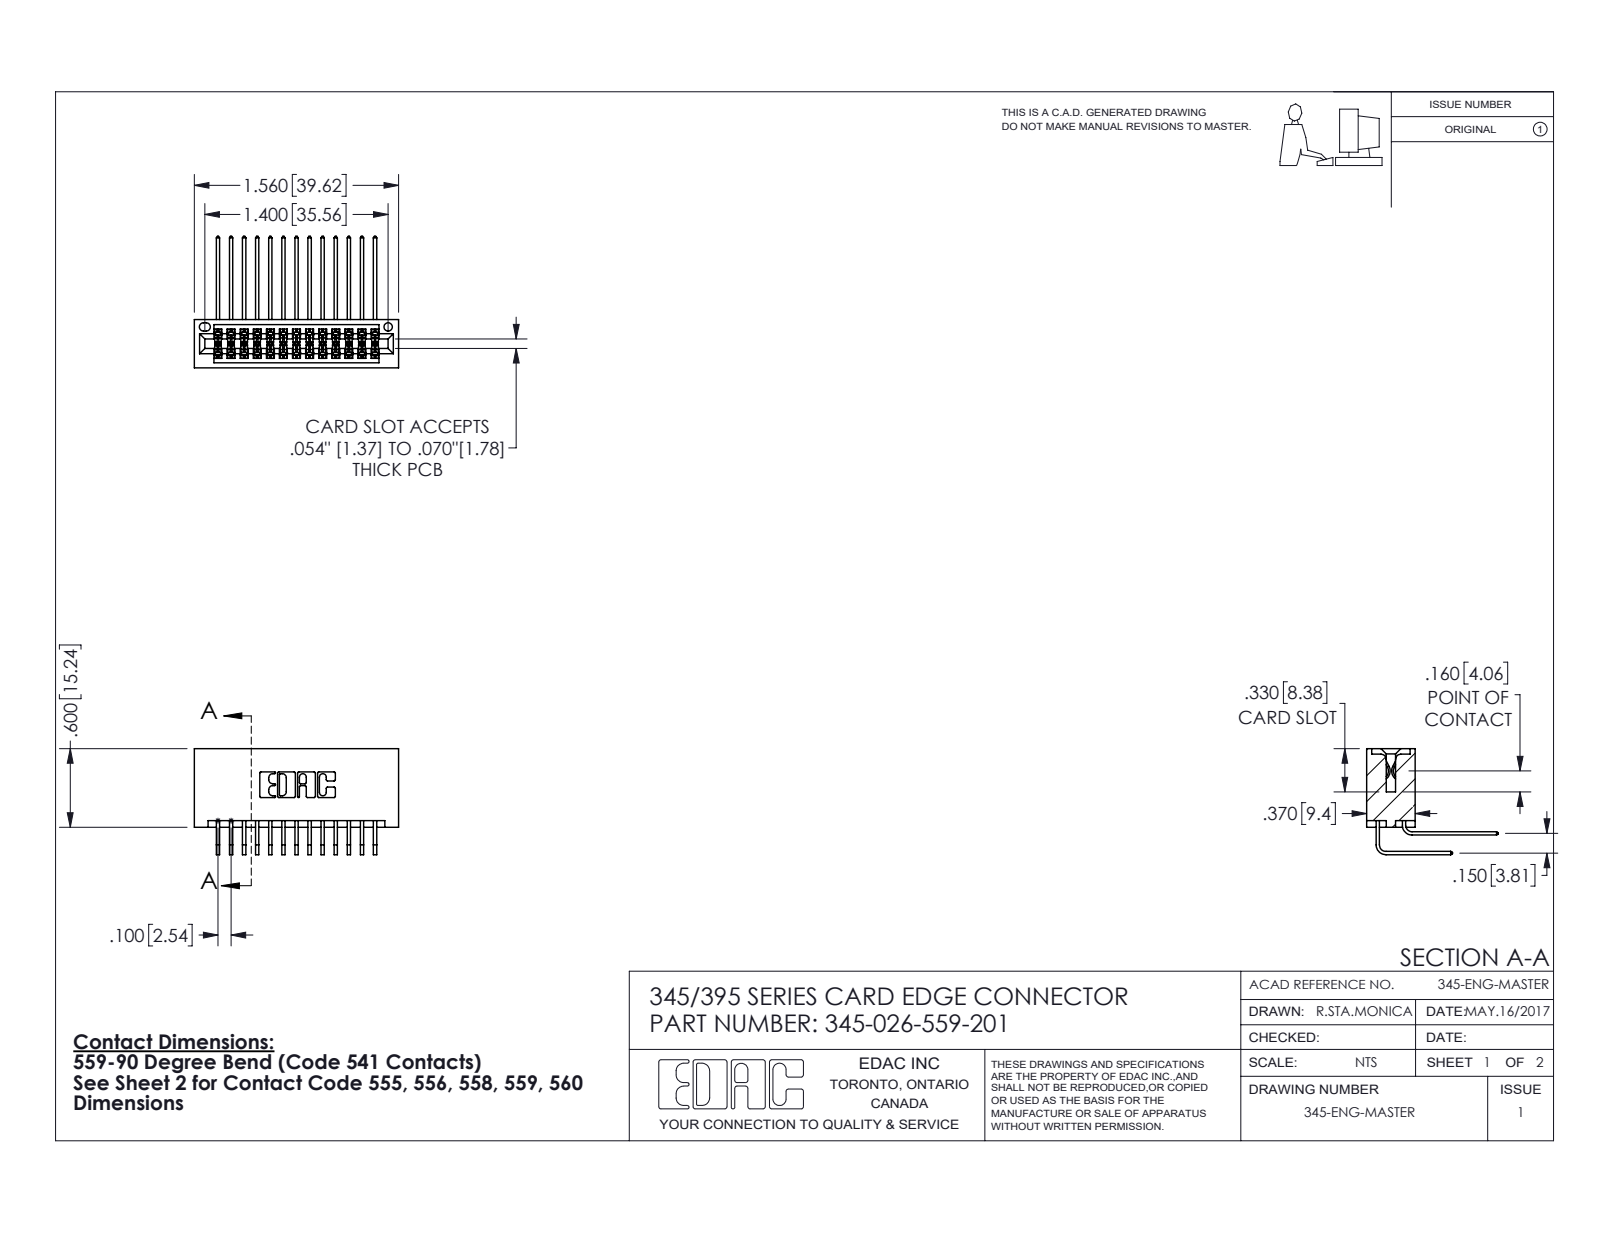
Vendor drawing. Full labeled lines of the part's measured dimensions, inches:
Part name (STEP PRODUCT): 345-292-001_559 Tail - 2; 345-026-559-201; 345 Part_No Mounting Lugs; 345-292-001_558 559 Tail - 1
STEP written by: SolidWorks 2016 (CONFIG_CONTROL_DESIGN)
Units: inches
Bodies: 27 solids, 1470 faces (986 planar, 484 cylindrical, 0 other)
Overall size (bounding box): 1.56 × 1.005 × 0.809
Volume: 0.265 in³ · Surface area: 10.65 in²
Round holes (diameter × count): ⌀0.064 ×1
Partial cylindrical surfaces — rounded edges, fillets, slot ends (radius × count): R0.006 ×51, R0.01 ×22, R0.007 ×6, R0.031 ×6, R0.026 ×3, R0.014 ×2, R0.019 ×2, R0.022 ×2
Main face-to-face distances: 0.072, 0.298, 0.2, 0.37, 0.098, 0.272, 0.025, 0.225, 0.15, 0.1
